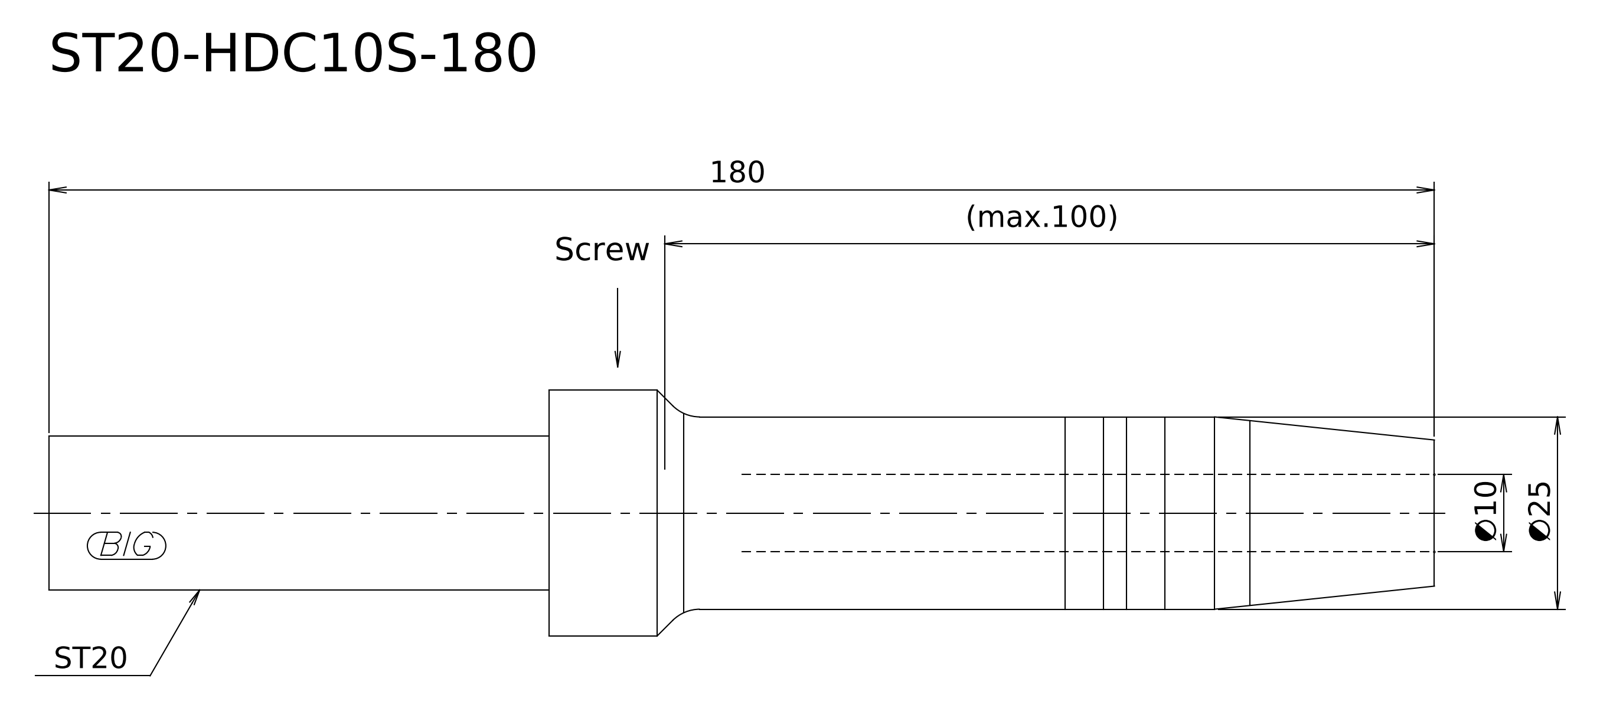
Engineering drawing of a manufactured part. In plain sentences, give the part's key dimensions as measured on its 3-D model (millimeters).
Its 3-D file was written by "Kubotek KeyCreator V8.5.1 (14335) (CONFIG_CONTROL_DESIGN)". It is 1 solid with 9 faces: 3 planar, 3 cylindrical and 3 other. Overall it measures 180 by 32 by 32 millimeters. Its volume is 78 814 cubic millimeters and its surface area 14 405 square millimeters. Round bosses or shafts: 1 of diameter 32, 1 of diameter 25, 1 of diameter 20. The main face-to-face distances are 65, 115, 180.
